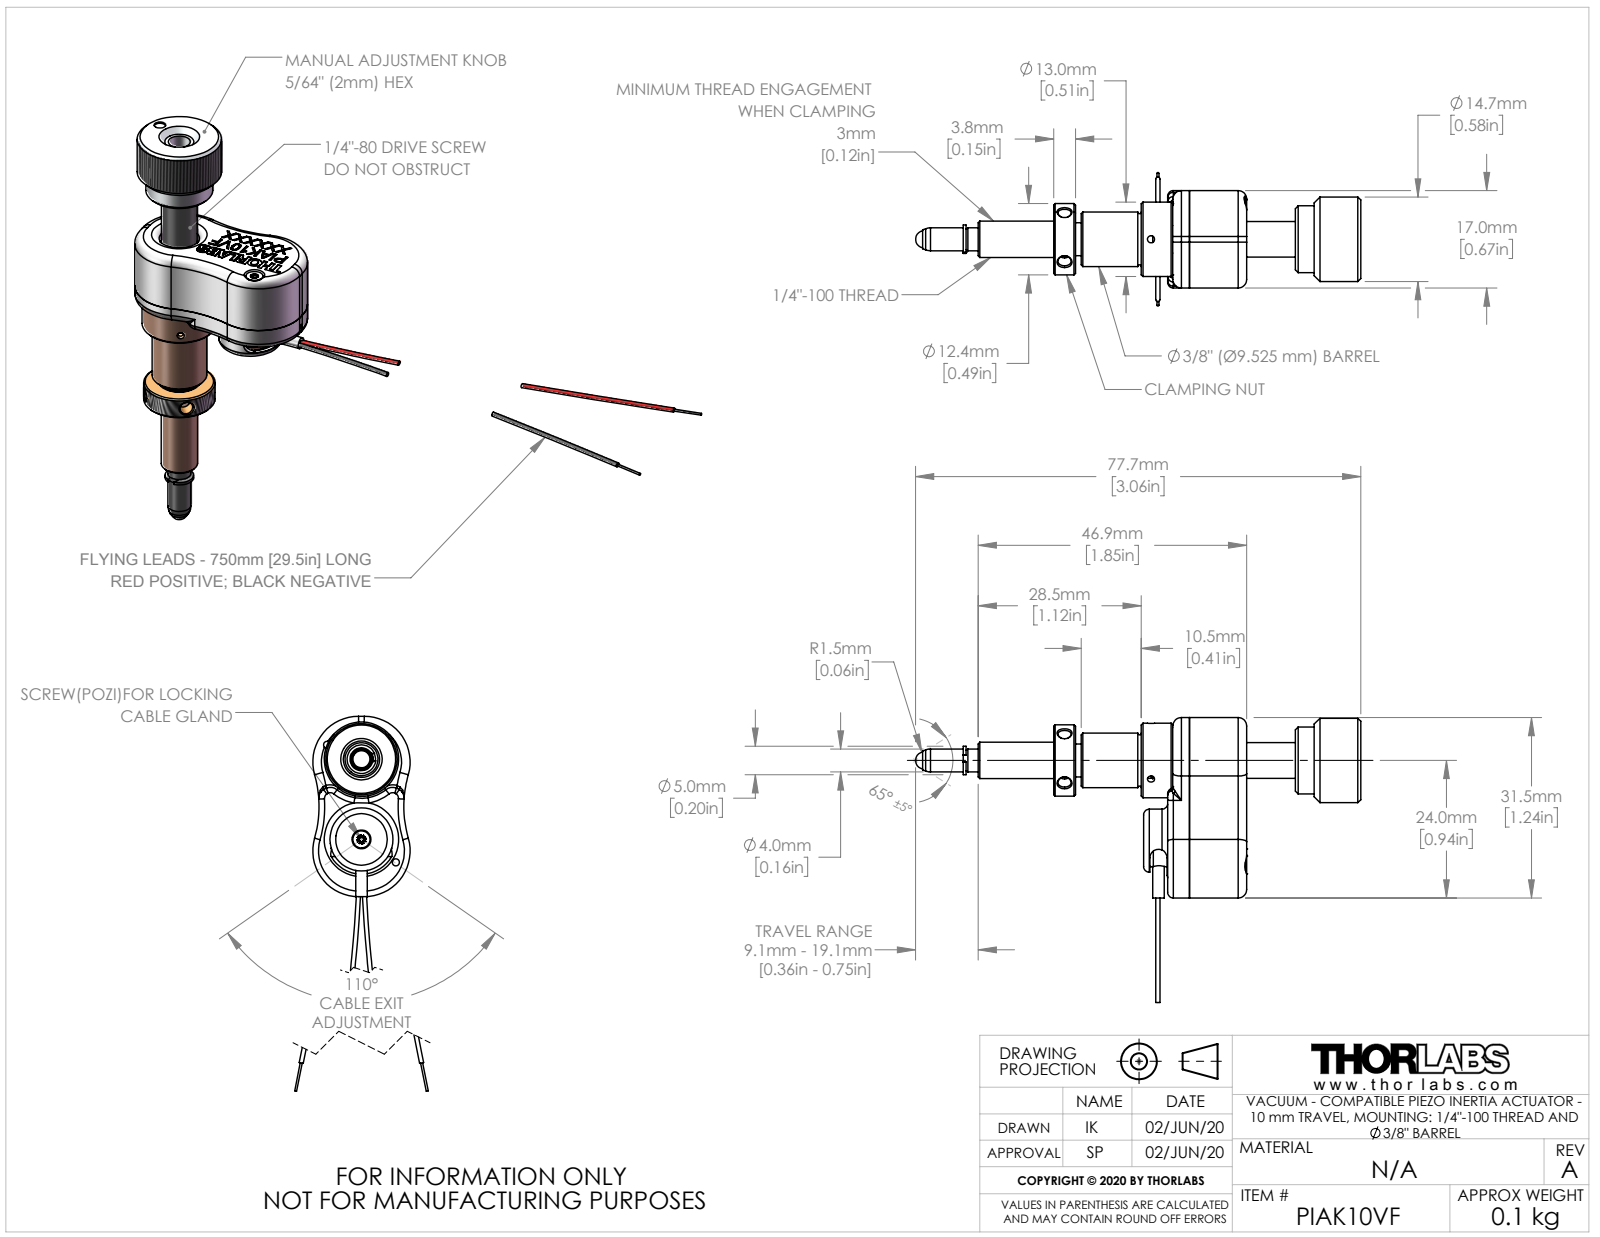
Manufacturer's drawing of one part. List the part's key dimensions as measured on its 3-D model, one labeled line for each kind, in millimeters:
Part name (STEP PRODUCT): PIAK10VF - VACUUM COMPATIBLE PIA - 1_4 THREAD, 10 mm TRAVEL12.IGS; PIAK10VF - VACUUM COMPATIBLE PIA - 1_4 THREAD, 10 mm TRAVEL17.IGS; PIAK10VF - VACUUM COMPATIBLE PIA - 1_4 THREAD, 10 mm TRAVEL13.IGS; PIAK10VF - VACUUM COMPATIBLE PIA - 1_4 THREAD, 10 mm TRAVEL22.IGS (+8 more)
STEP written by: SolidWorks 2019 (AUTOMOTIVE_DESIGN)
Units: millimetres
Bodies: 19 solids, 981 faces (0 planar, 0 cylindrical, 981 other)
Overall size (bounding box): 104.54 × 77.73 × 23.33
Volume: 4 829 mm³ · Surface area: 9 576 mm²
